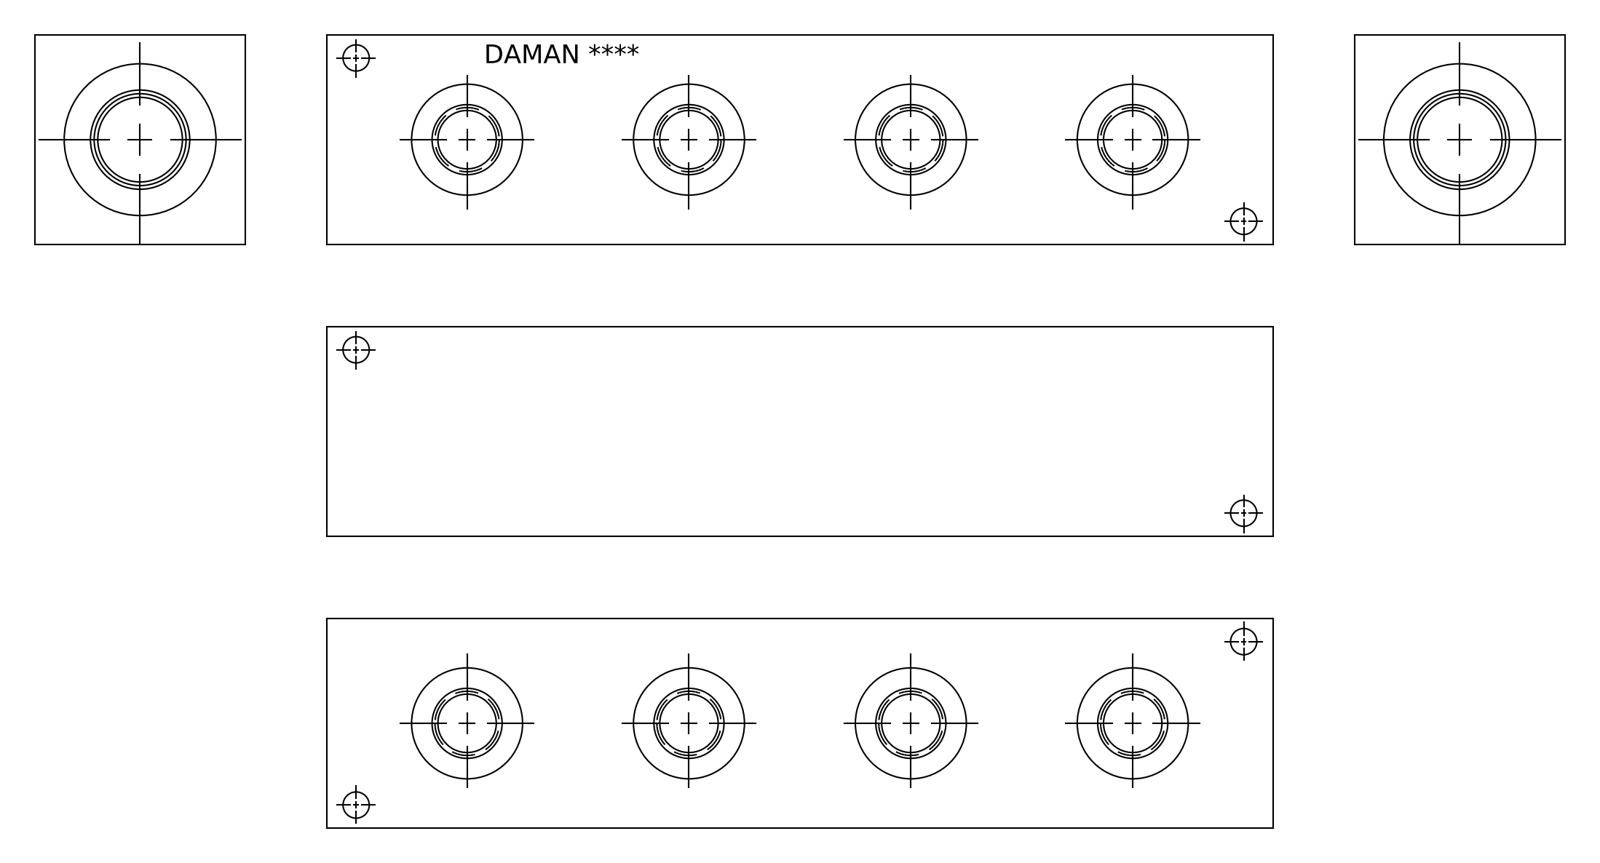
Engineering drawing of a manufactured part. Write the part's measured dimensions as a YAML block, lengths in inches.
part_name: "Part_+H1800408S_3D"
step_written_by: "Autodesk Inventor 2020 (AUTOMOTIVE_DESIGN)"
units: inches
bodies: {solids: 1, faces: 438, planar: 241, cylindrical: 58, other: 139}
overall_size: [10.125, 2.25, 2.25]
volume: 45.26
surface_area: 131
round_holes:
  - {diameter: 0.281, count: 4}
  - {diameter: 0.625, count: 4}
  - {diameter: 0.689, count: 4}
  - {diameter: 0.75, count: 4}
  - {diameter: 0.758, count: 4}
  - {diameter: 1.206, count: 4}
  - {diameter: 0.906, count: 1}
  - {diameter: 0.981, count: 1}
  - {diameter: 1.063, count: 1}
  - {diameter: 1.063, count: 1}
  - {diameter: 1.08, count: 1}
  - {diameter: 1.655, count: 1}
face_to_face_distances: [2.25, 0.031, 2.219, 10.125, 2.188, 10.094, 10.063, 0.593, 1.657, 0.562]
hole_center_spacings: [2.375, 4.75, 9.66, 1.474, 1.476, 2.375, 3.668, 3.669]
